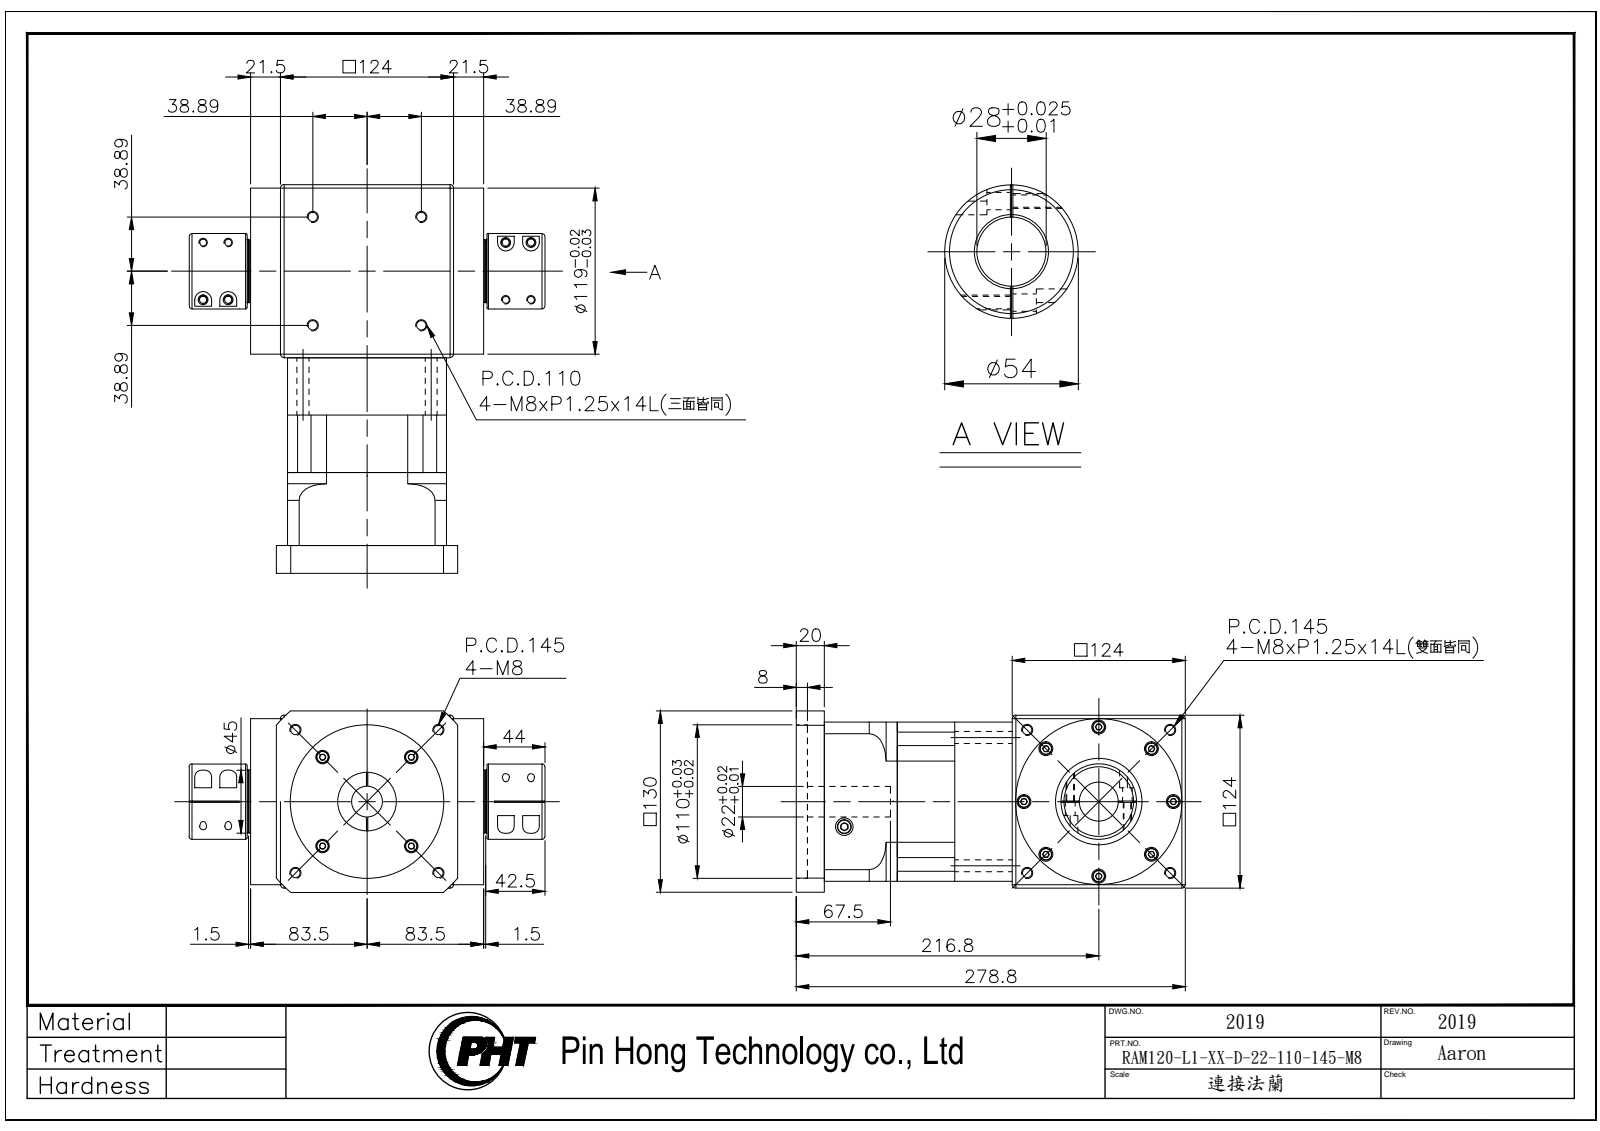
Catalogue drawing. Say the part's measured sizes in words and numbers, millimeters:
The part is named "RAM120-L1-XX-D-22-110-145-M8_2019". Its 3-D file was written by "SolidWorks 2016 (AUTOMOTIVE_DESIGN)". It is 4 solids with 1384 faces: 706 planar, 438 cylindrical and 240 other. Overall it measures 278.8 by 255 by 130 millimeters. Its volume is 4 159 000 cubic millimeters and its surface area 395 188 square millimeters. Round holes: 16 of diameter 6.8, 12 of diameter 9.5, 8 of diameter 5.3, 8 of diameter 7, 8 of diameter 9, 8 of diameter 14, 4 of diameter 4.2, 4 of diameter 5.5, 4 of diameter 8.6, 2 of diameter 12.7, 1 of diameter 22, 1 of diameter 28. Round bosses or shafts: 12 of diameter 13, 12 of diameter 8.5, 8 of diameter 10.5, 8 of diameter 10, 8 of diameter 6, 1 of diameter 119, 1 of diameter 62, 1 of diameter 54. Partial cylindrical surfaces (rounded edges, fillets, slot ends): 8 of radius 3.52, 8 of radius 5.5, 4 of radius 7, 1 of radius 64, 1 of radius 75, 1 of radius 85, 1 of radius 86.2. The main face-to-face distances are 124, 5, 119, 41.5, 114, 3, 82.5, 41, 8, 206.5. The hole center spacings are 59, 10, 15.4, 17.24, 19.42, 21.77, 39.8, 51.28.
